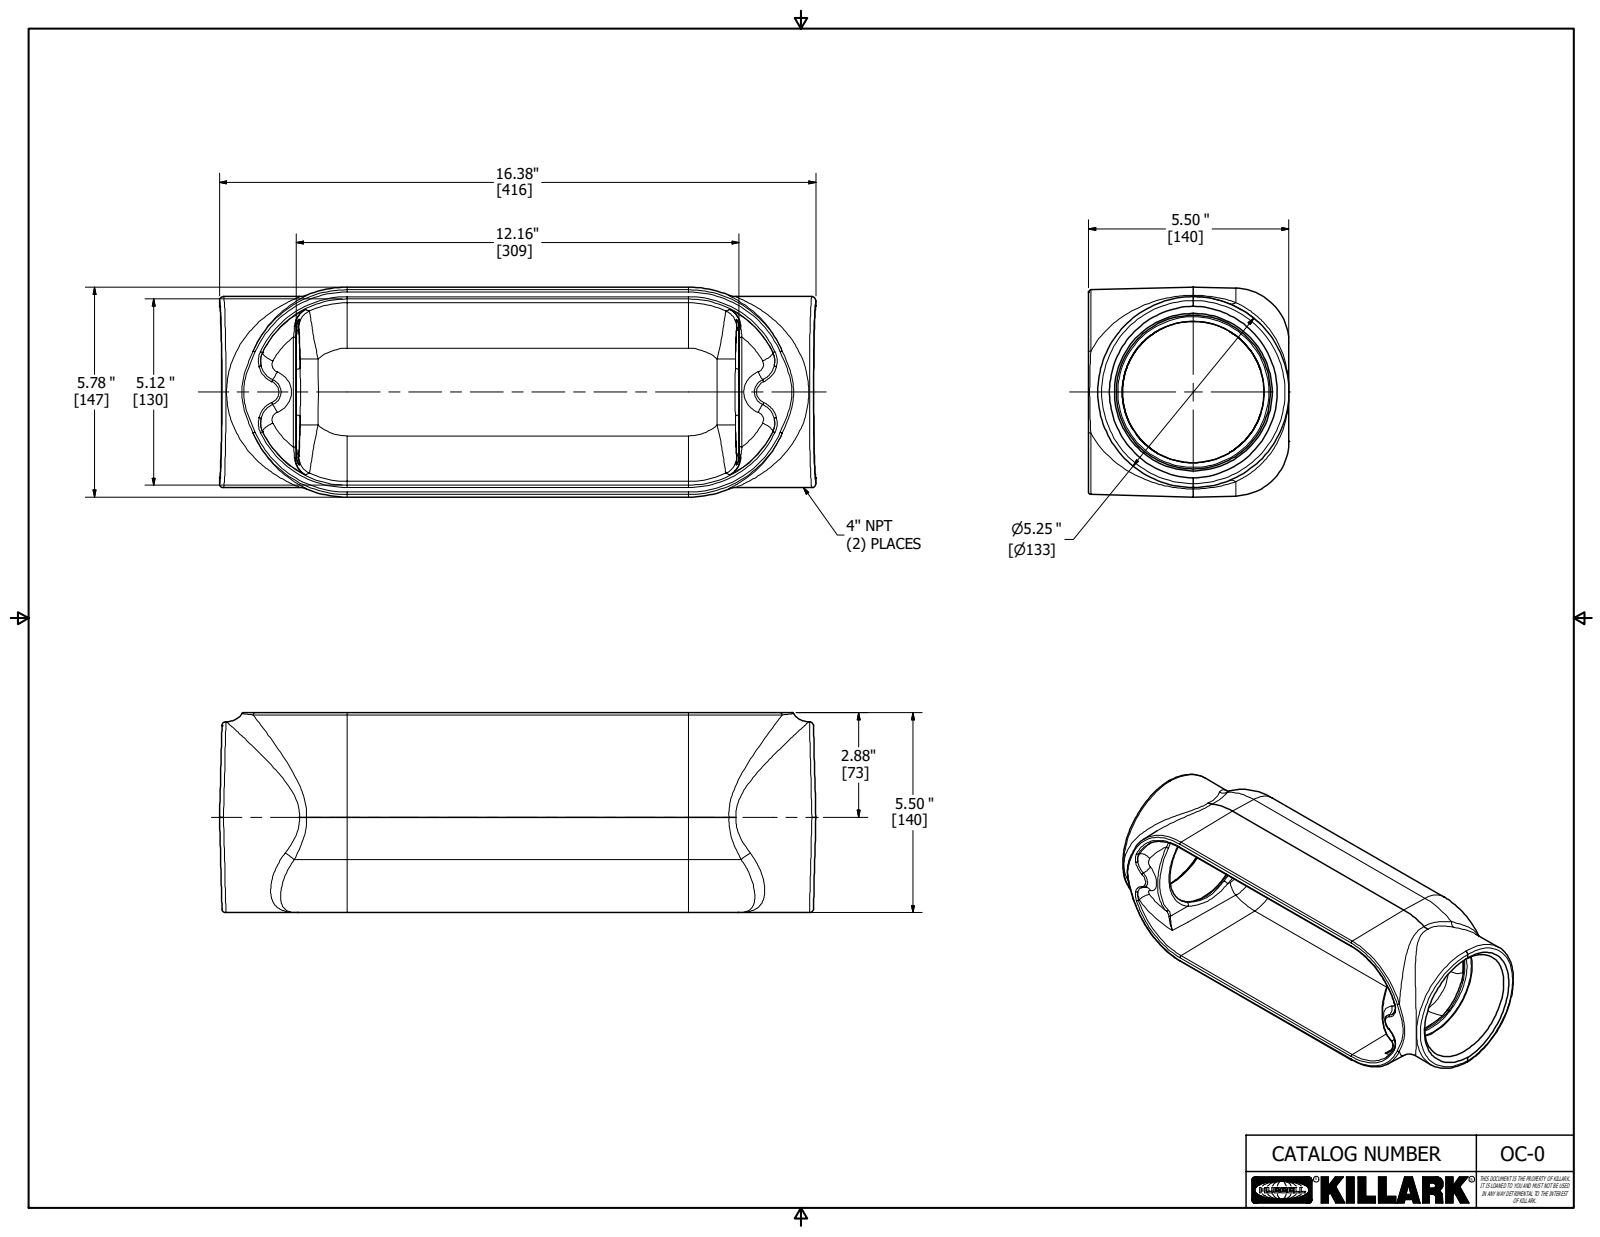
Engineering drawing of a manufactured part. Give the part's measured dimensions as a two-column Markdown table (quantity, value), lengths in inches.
| quantity | value |
| --- | --- |
| part name | 10792-2 |
| STEP written by | Autodesk Inventor 2018 (AUTOMOTIVE_DESIGN) |
| units | inches |
| bodies | 1 solid, 1087 faces (541 planar, 34 cylindrical, 512 other) |
| overall size | 16.375 × 5.776 × 5.508 |
| volume | 91.89 in³ |
| surface area | 530.8 in² |
| round holes (diameter × count) | 0.07 × 1, 0.611 × 1 |
| round bosses / shafts (diameter × count) | 5.25 × 1, 0.75 × 1, 0.083 × 1 |
| partial cylindrical surfaces (radius × count) | 0.031 × 4, 0.062 × 4, 1.25 × 2, 1.5 × 2, 0.008 × 1, 0.013 × 1, 0.024 × 1, 0.094 × 1 |
| main face-to-face distances | 5.375, 5.375, 0.187, 5.776, 0.401, 0.4, 5.5, 5.313, 16.374, 0.031 |
| hole center spacings | 0.183 |
